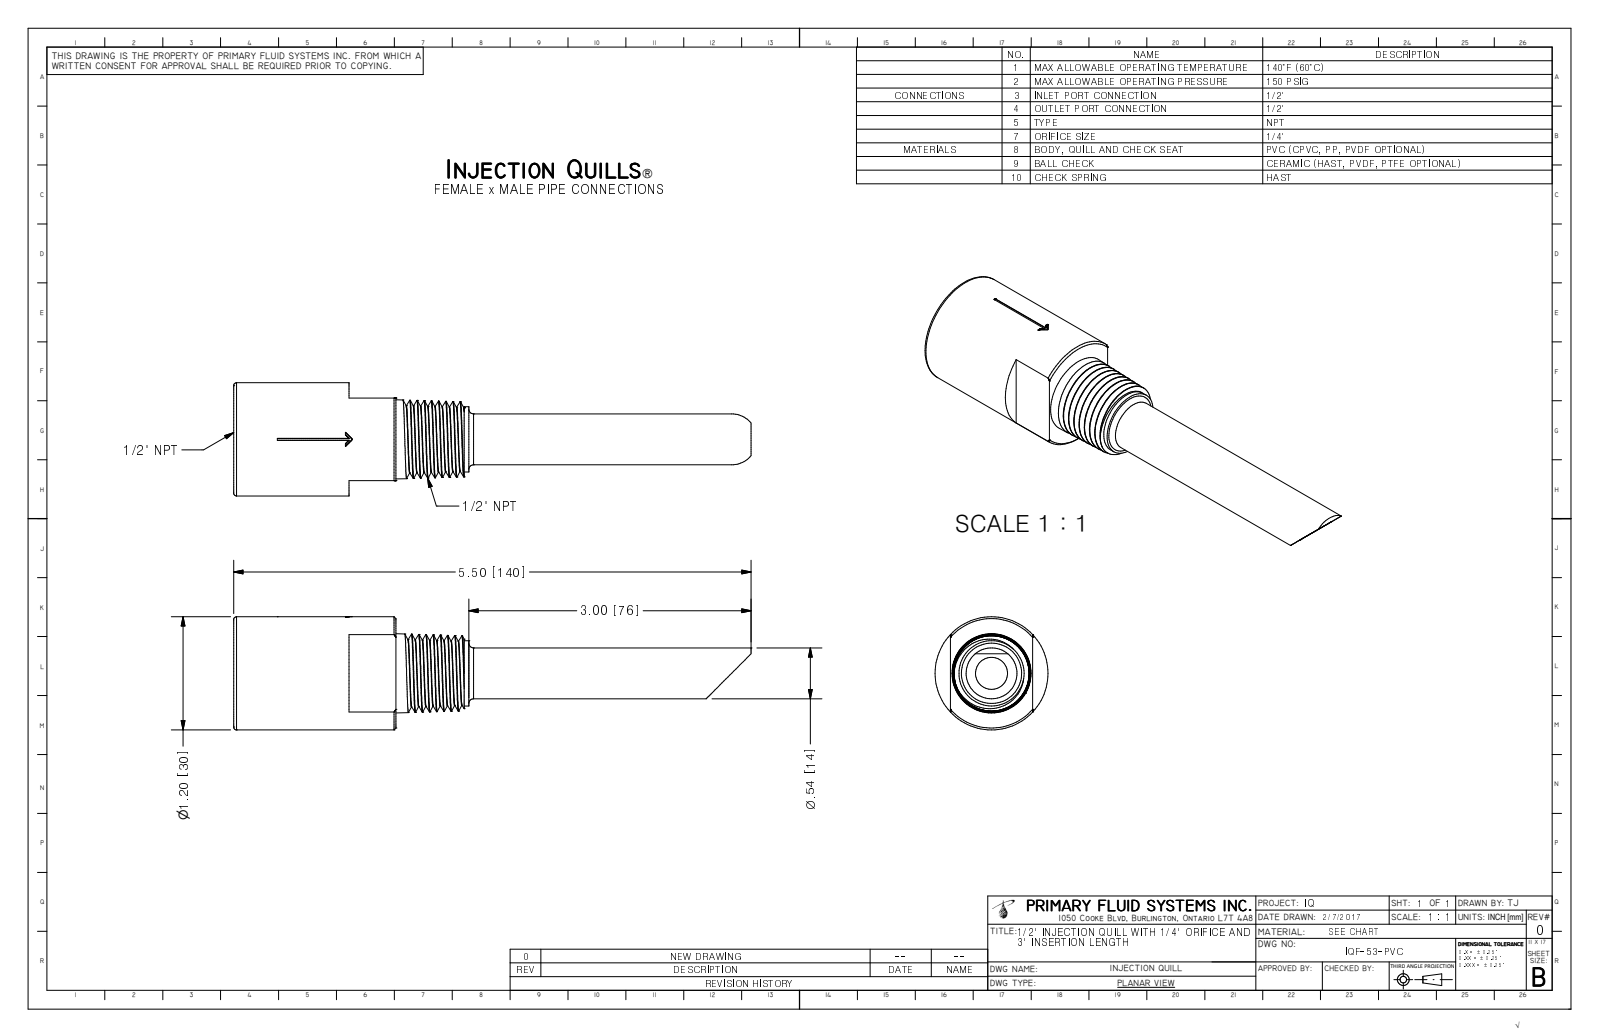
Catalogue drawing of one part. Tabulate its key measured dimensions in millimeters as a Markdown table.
| quantity | value |
| --- | --- |
| part name | IQF-53-PVC_R0 |
| STEP written by | Autodesk Inventor 2009 (AUTOMOTIVE_DESIGN) |
| units | millimeters |
| bodies | 1 solid, 74 faces (36 planar, 7 cylindrical, 31 other) |
| overall size | 139.7 × 30.5 × 30.5 |
| volume | 32 640 mm³ |
| surface area | 16 190 mm² |
| round holes (diameter × count) | 8.6 × 1, 11.1 × 1, 17.9 × 1 |
| round bosses / shafts (diameter × count) | 30.5 × 1, 17.6 × 1, 13.7 × 1 |
| partial cylindrical surfaces (radius × count) | 15.1 × 1 |
| main face-to-face distances | 22.2, 43.8, 12.7, 31.1, 12.1, 19.1, 31.8, 16.5, 24.8, 15.2 |
